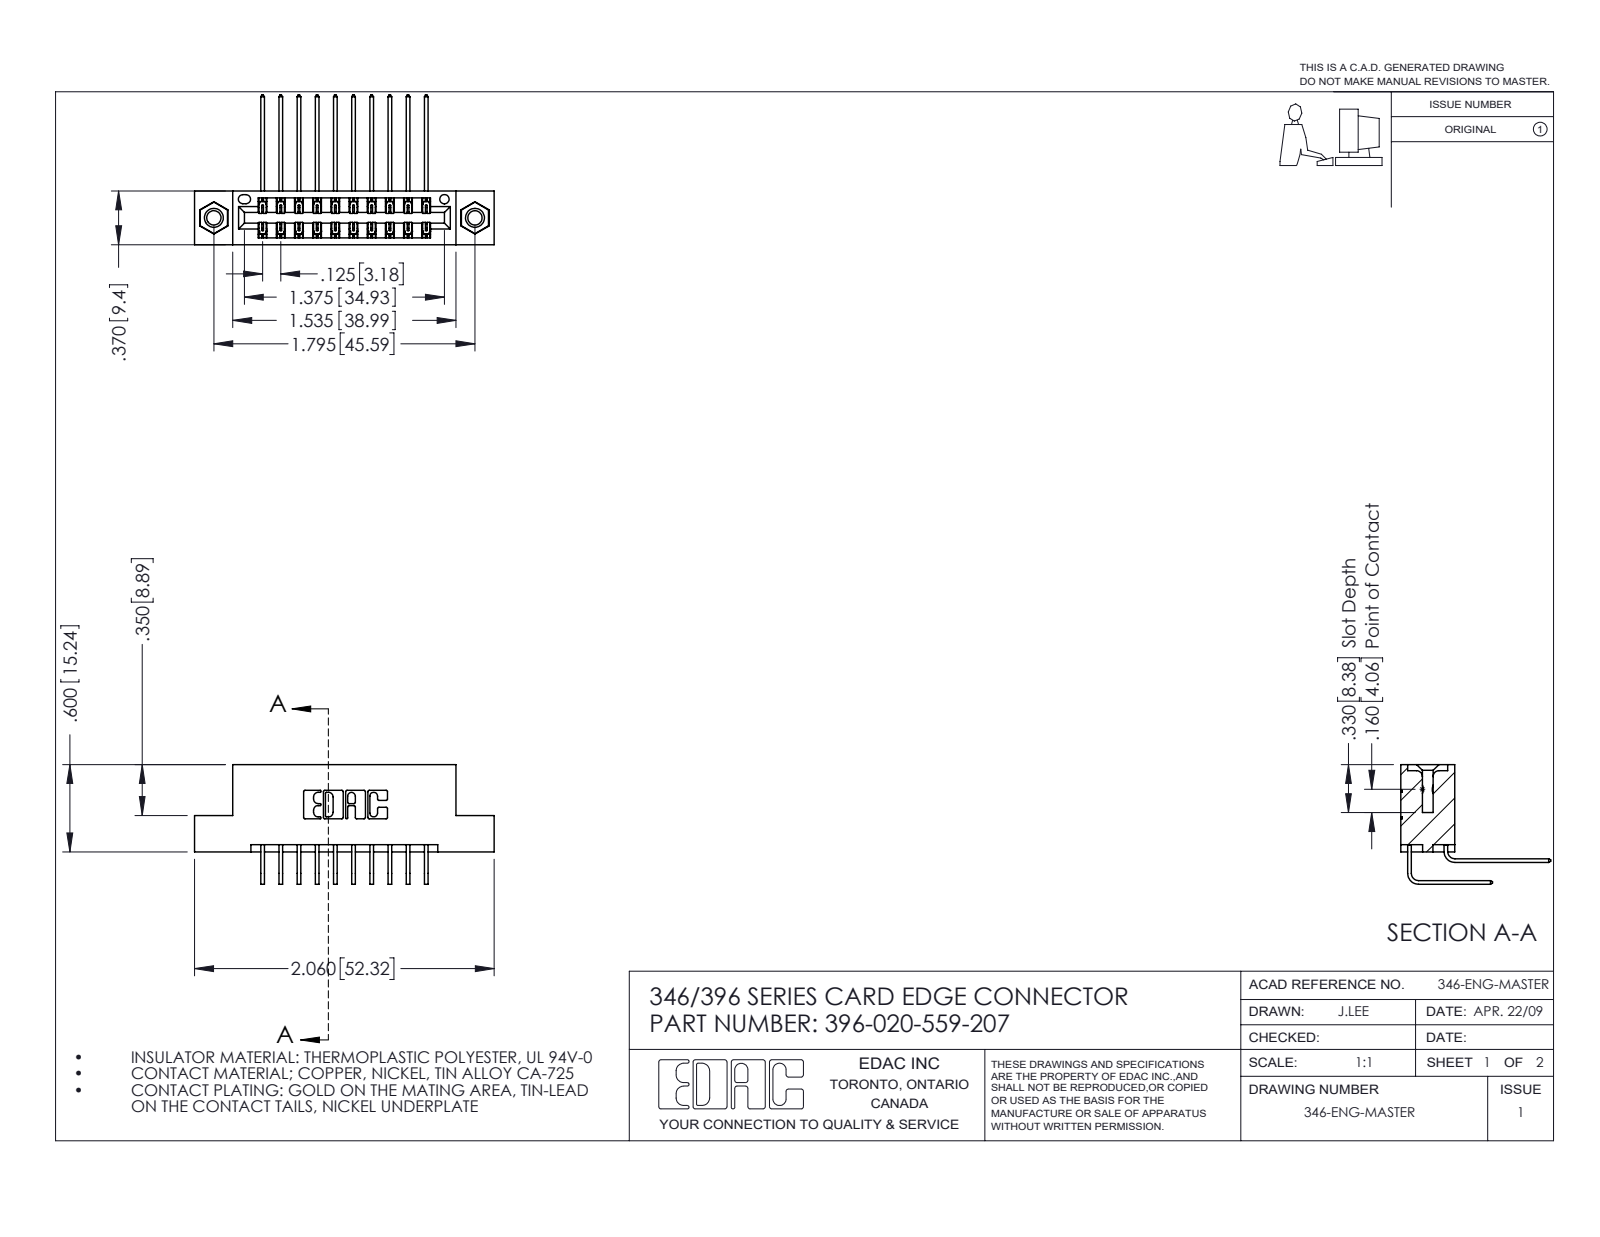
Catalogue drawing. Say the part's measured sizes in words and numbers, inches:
The part is named "345-250-001_345-250-005-103; 396-020-559-207; 346 Part_Flush Mounting Lugs - 0.156 Dia-TI; 345-292-001_559 Tail - 2 (+1 more)". Its 3-D file was written by "SolidWorks 2016 (CONFIG_CONTROL_DESIGN)". It is 23 solids with 1262 faces: 848 planar, 398 cylindrical and 16 other. Overall it measures 2.06 by 1.03 by 0.823 inches. Its volume is 0.302 cubic inches and its surface area 10.69 square inches. Round holes: 2 of diameter 0.098, 2 of diameter 0.125, 2 of diameter 0.156, 1 of diameter 0.064. Round bosses or shafts: 2 of diameter 0.155. Partial cylindrical surfaces (rounded edges, fillets, slot ends): 30 of radius 0.006, 22 of radius 0.01, 6 of radius 0.007, 6 of radius 0.031, 3 of radius 0.026, 2 of radius 0.014, 2 of radius 0.022, 2 of radius 0.024. The main face-to-face distances are 0.25, 0.048, 0.322, 0.37, 0.025, 0.072, 0.298, 0.275, 0.148, 0.222. The hole center spacings are 0.246, 1.59, 1.795.
